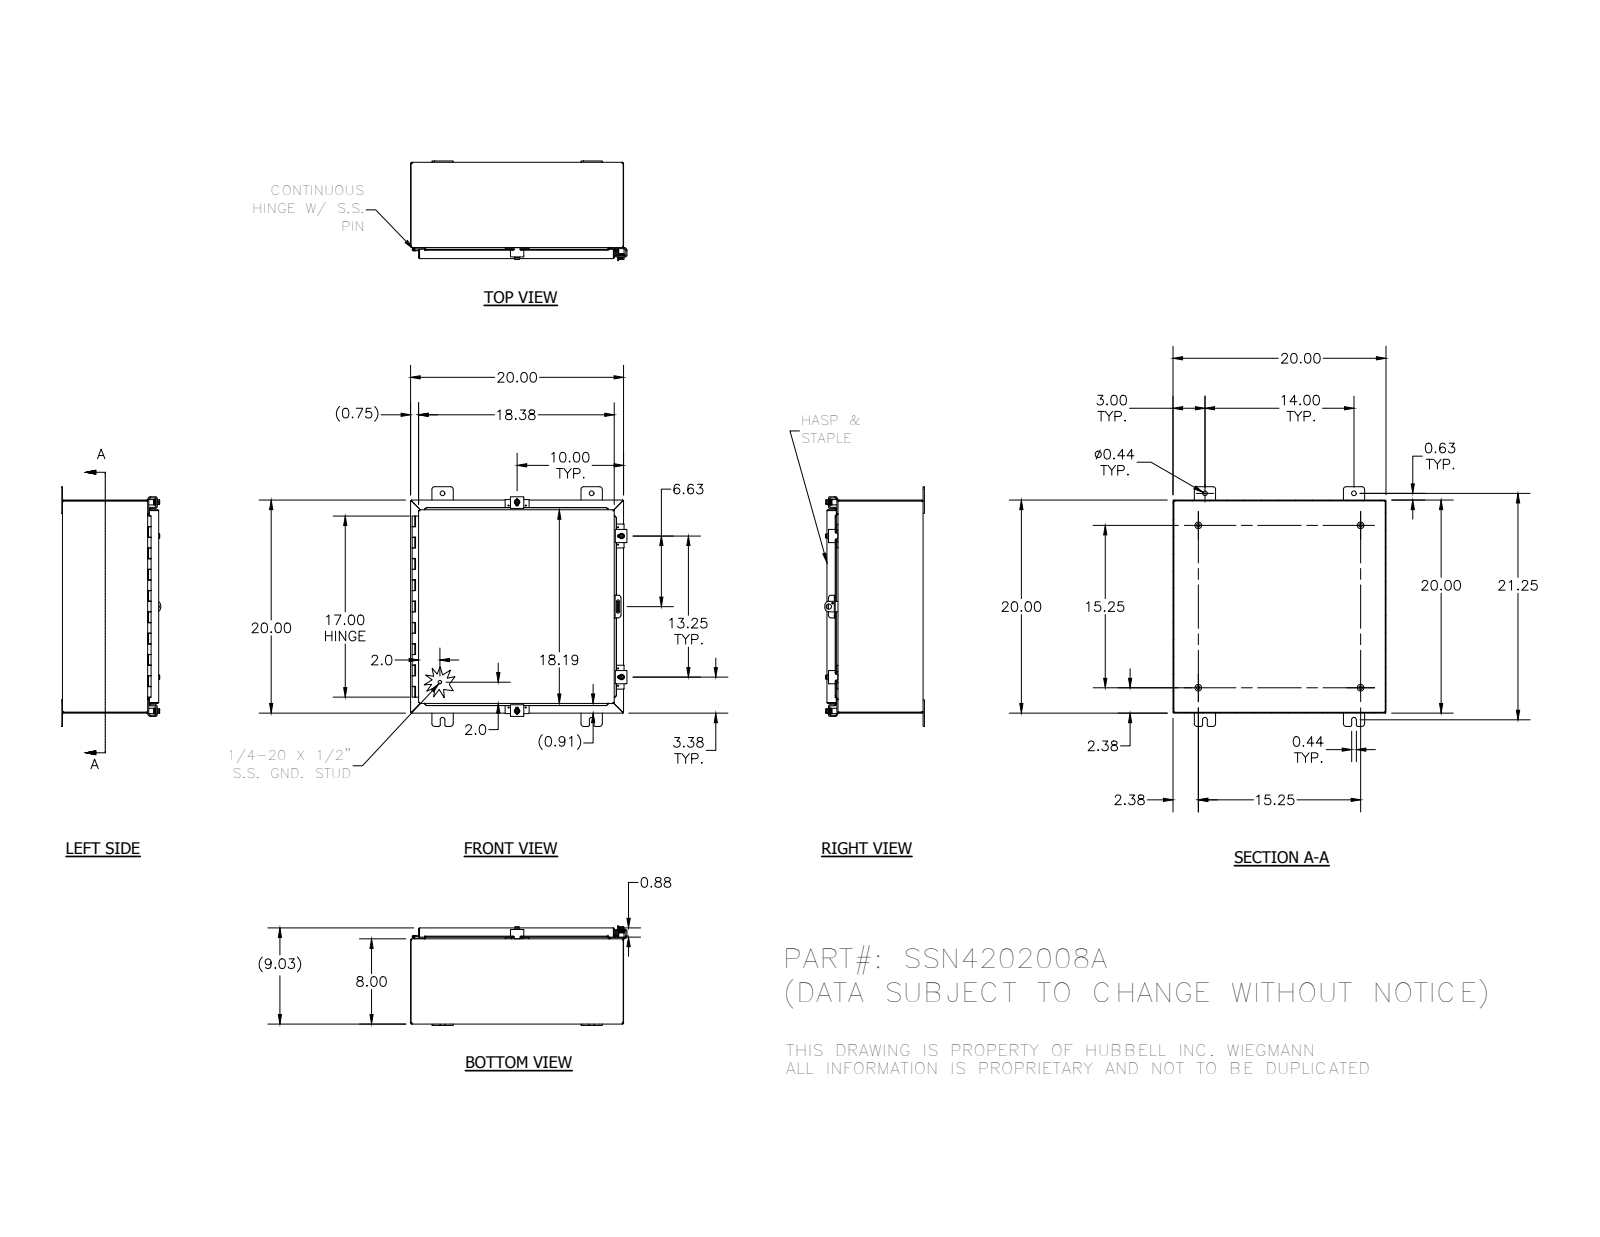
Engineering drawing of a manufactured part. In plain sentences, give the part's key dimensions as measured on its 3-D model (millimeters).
The part is named "34871; 32874-20P; 32874-20L; 38846 (+8 more)". Its 3-D file was written by "SolidWorks 2014 (AUTOMOTIVE_DESIGN)". It is 37 solids with 1428 faces: 575 planar, 612 cylindrical and 241 other. Overall it measures 571.5 by 513.5 by 237.6 millimeters. Its volume is 2 181 000 cubic millimeters and its surface area 2 246 000 square millimeters. Round holes: 8 of diameter 2.8, 4 of diameter 5.4, 4 of diameter 7.1, 4 of diameter 7.6, 4 of diameter 11.1, 1 of diameter 3.2, 1 of diameter 4, 1 of diameter 12.7. Round bosses or shafts: 6 of diameter 6.4, 4 of diameter 15.9, 4 of diameter 13.2, 4 of diameter 12.7, 4 of diameter 8.9, 4 of diameter 8.4, 1 of diameter 8.6, 1 of diameter 3. Partial cylindrical surfaces (rounded edges, fillets, slot ends): 49 of radius 0.8, 33 of radius 3.2, 29 of radius 6.4, 23 of radius 0.8, 23 of radius 2.7, 14 of radius 1.6, 8 of radius 1.8, 8 of radius 3.6. The main face-to-face distances are 1.9, 227.6, 506.1, 225.7, 229.4, 504.2, 508, 201.3, 26.2, 203.2. The hole center spacings are 22.3, 490.4, 336.6, 22.3, 41.3, 41.3, 157.2, 159.8.
